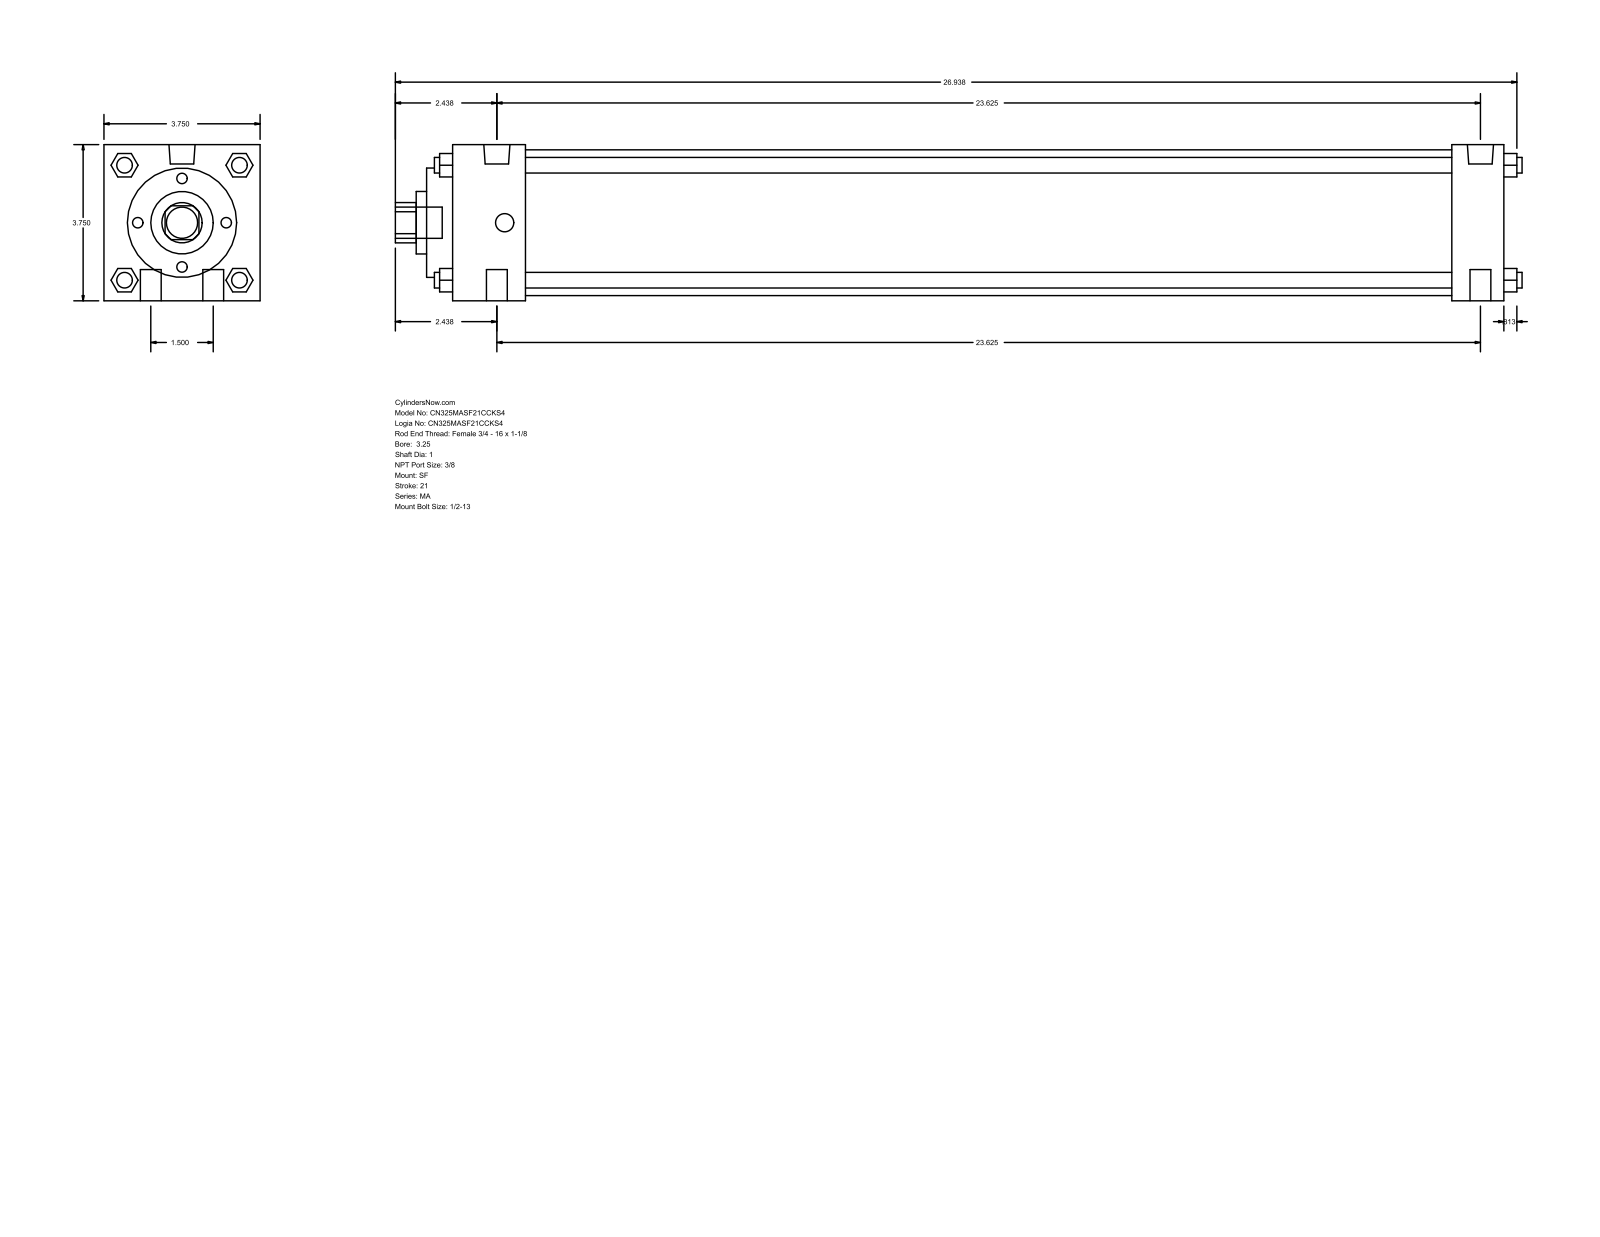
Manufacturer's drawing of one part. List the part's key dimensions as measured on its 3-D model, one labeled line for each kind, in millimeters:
Part name (STEP PRODUCT): MA_SF__0325_1
STEP written by: GSSL Pune (CONFIG_CONTROL_DESIGN)
Units: millimetres
Bodies: 0 solids, 126 faces (95 planar, 31 cylindrical, 0 other)
Overall size (bounding box): 687.39 × 95.25 × 95.25
Round holes (diameter × count): ⌀25.4 ×1, ⌀38.1 ×1, ⌀66.67 ×1, ⌀88.9 ×1
Round bosses / shafts (diameter × count): ⌀12.7 ×4, ⌀9.53 ×4, ⌀15.93 ×2, ⌀11.11 ×2, ⌀19.05 ×1
Partial cylindrical surfaces — rounded edges, fillets, slot ends (radius × count): R12.29 ×1
Main face-to-face distances: 95.24, 641.35, 657.22, 15.87, 609.6, 31.75, 44.46, 565.14, 596.89, 60.33
